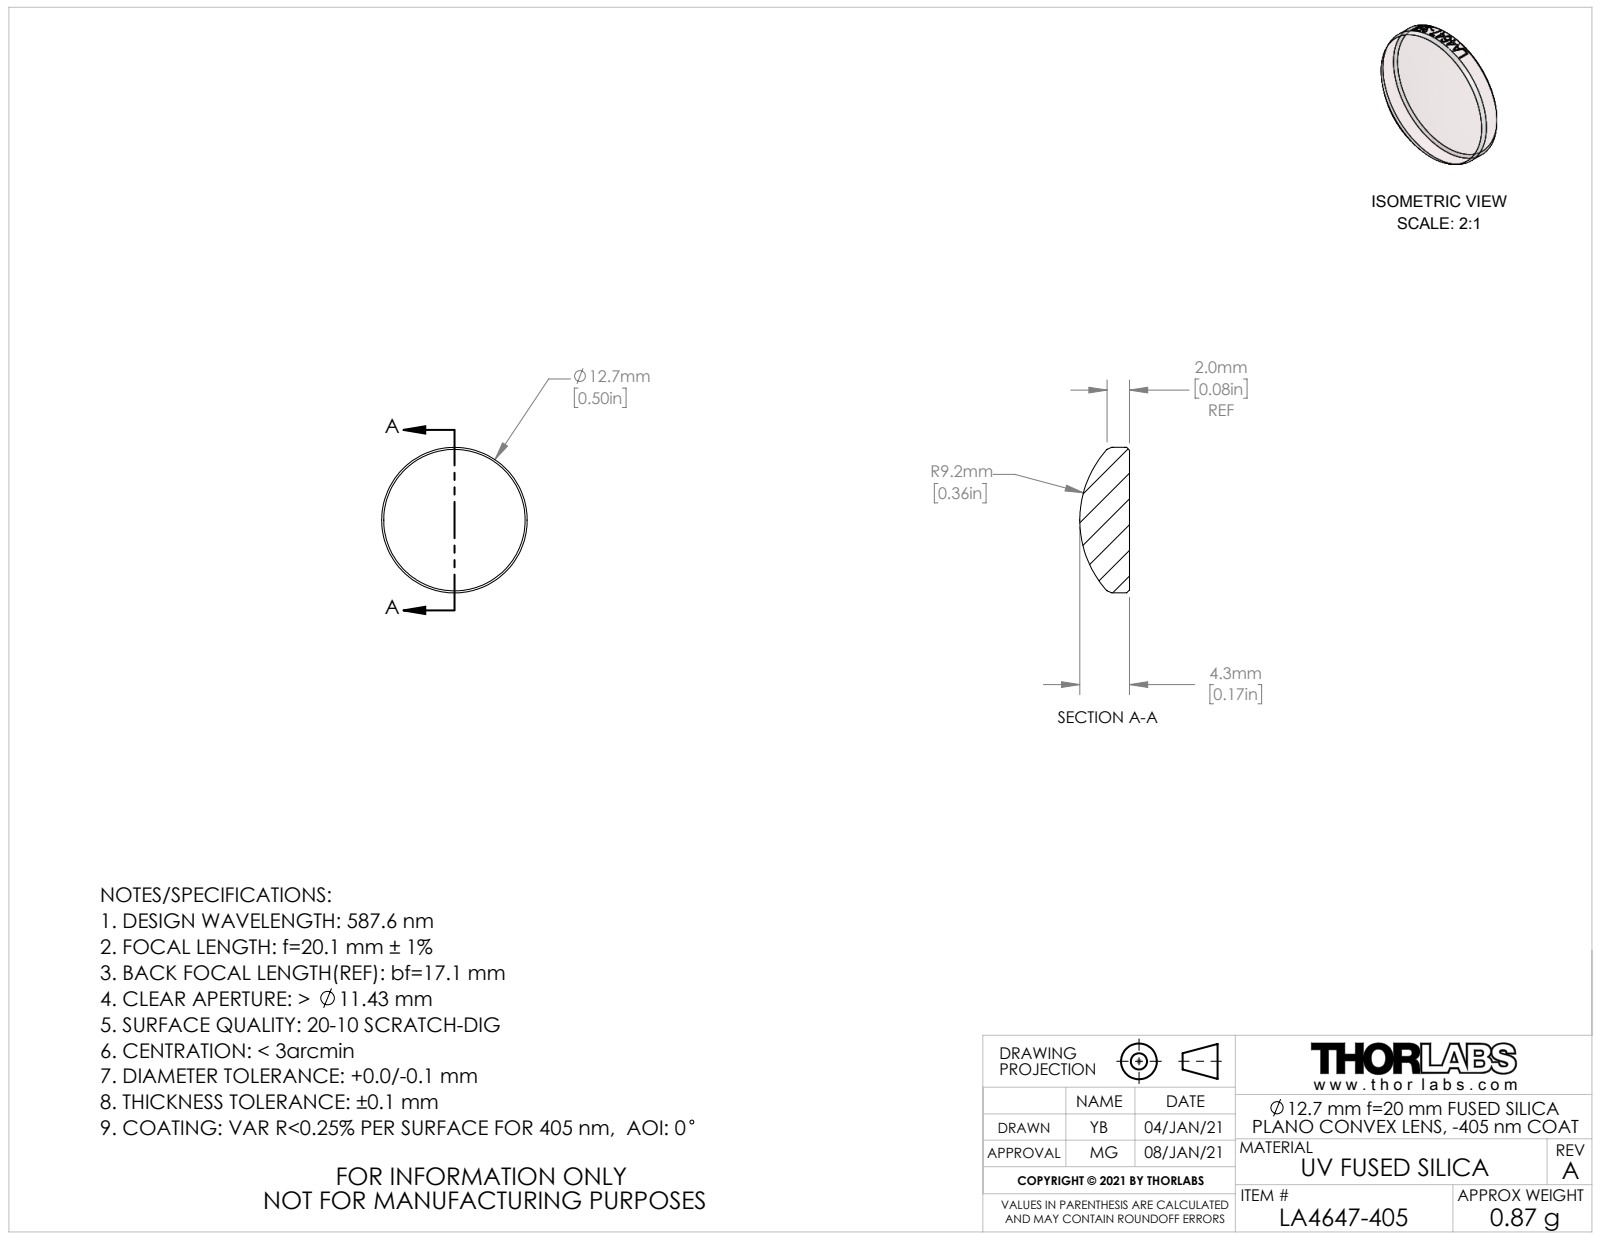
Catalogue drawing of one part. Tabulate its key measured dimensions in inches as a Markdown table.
| quantity | value |
| --- | --- |
| part name | CTN016836; CTN016816-E0W |
| STEP written by | SolidWorks 2018 (AUTOMOTIVE_DESIGN) |
| units | inches |
| bodies | 1 solid, 25 faces (1 planar, 18 cylindrical, 6 other) |
| overall size | 0.5 × 0.5 × 0.171 |
| volume | 0.024 in³ |
| surface area | 0.524 in² |
| round bosses / shafts (diameter × count) | 0.5 × 1 |
